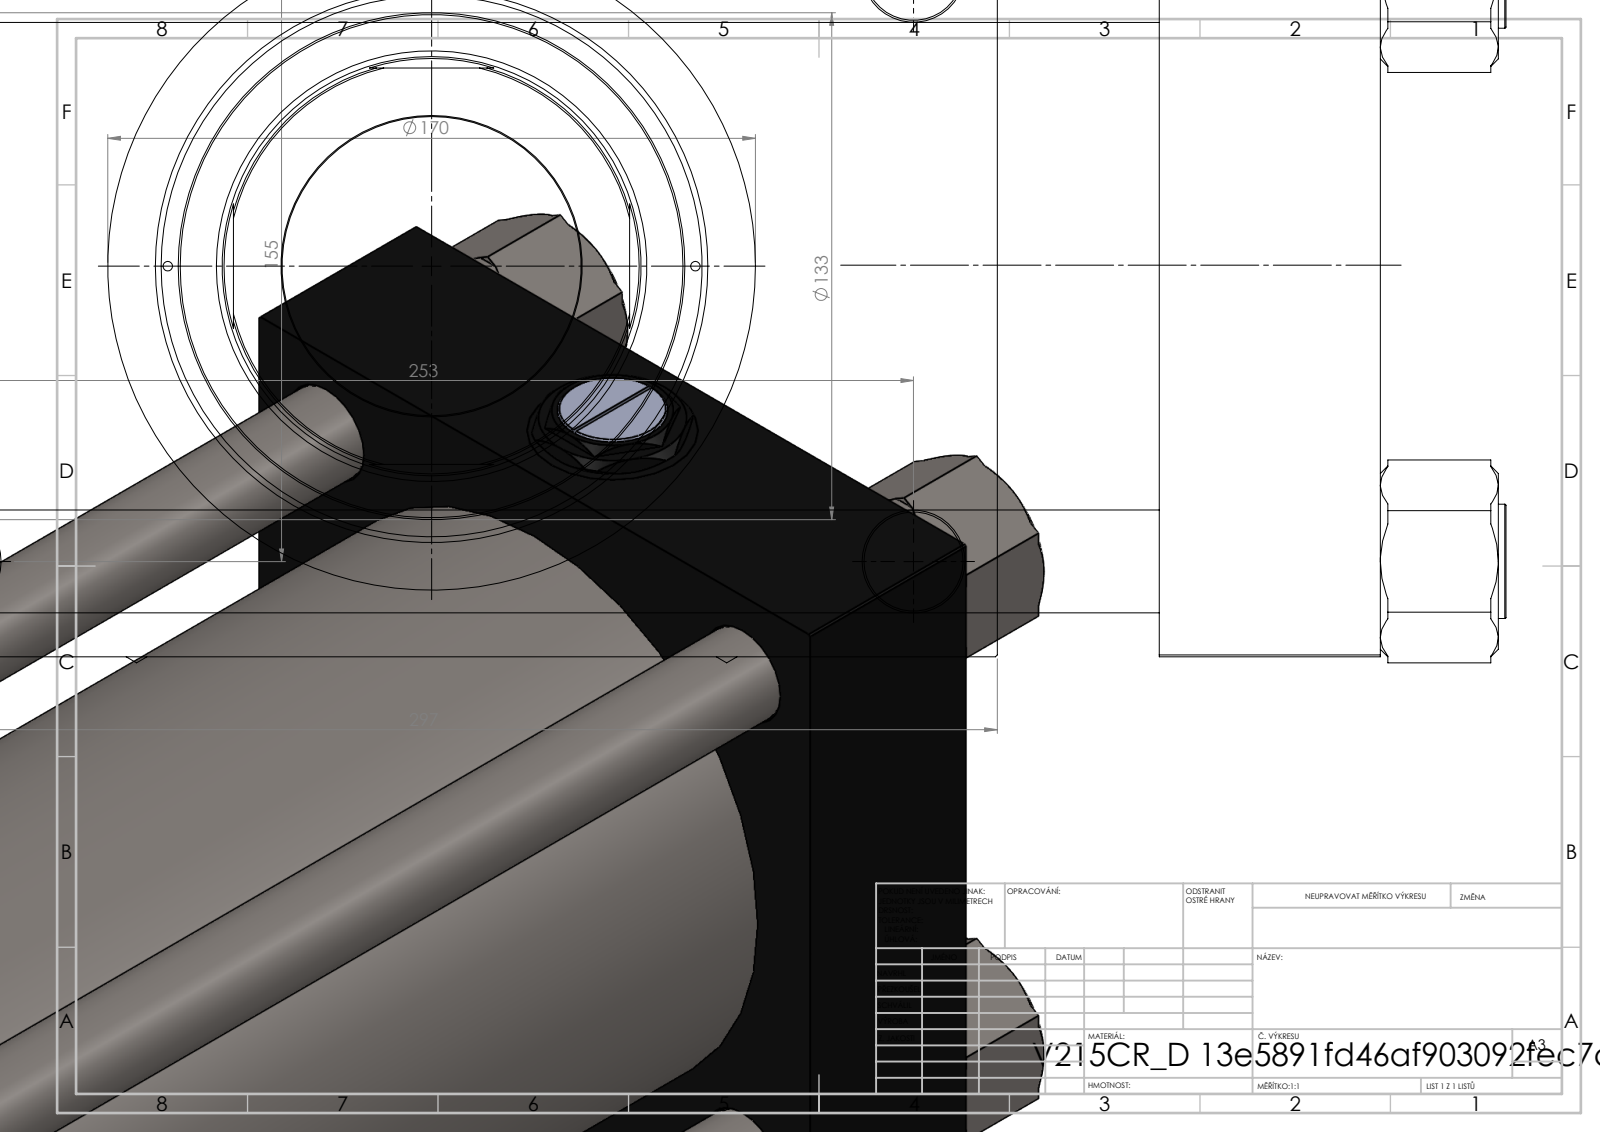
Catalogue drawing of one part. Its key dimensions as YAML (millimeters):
part_name: "V215_VC_A; V215CR_D_Body; V215CR_VCP_D; V215CR_D_TYCINKA (+2 more)"
step_written_by: "SolidWorks 2019 (CONFIG_CONTROL_DESIGN)"
units: millimeters
bodies: {solids: 13, faces: 1260, planar: 595, cylindrical: 103, other: 562}
overall_size: [626, 297, 213.57]
volume: 12490000
surface_area: 1355000
round_holes:
  - {diameter: 26, count: 4}
  - {diameter: 27, count: 4}
  - {diameter: 33.24, count: 4}
  - {diameter: 45, count: 4}
  - {diameter: 7, count: 3}
  - {diameter: 2.5, count: 2}
  - {diameter: 78.5, count: 1}
  - {diameter: 110, count: 1}
  - {diameter: 113, count: 1}
  - {diameter: 120, count: 1}
  - {diameter: 142, count: 1}
  - {diameter: 160, count: 1}
round_bosses_or_shafts:
  - {diameter: 30, count: 4}
  - {diameter: 170, count: 1}
  - {diameter: 166, count: 1}
  - {diameter: 133, count: 1}
partial_cylinders:
  - {radius: 54, count: 1}
face_to_face_distances: [58, 480, 422, 478, 56, 536, 205, 46, 251, 72]
hole_center_spacings: [49.05, 77.88, 96.35, 109.53, 148.35, 154.9, 162.53, 165.89]
